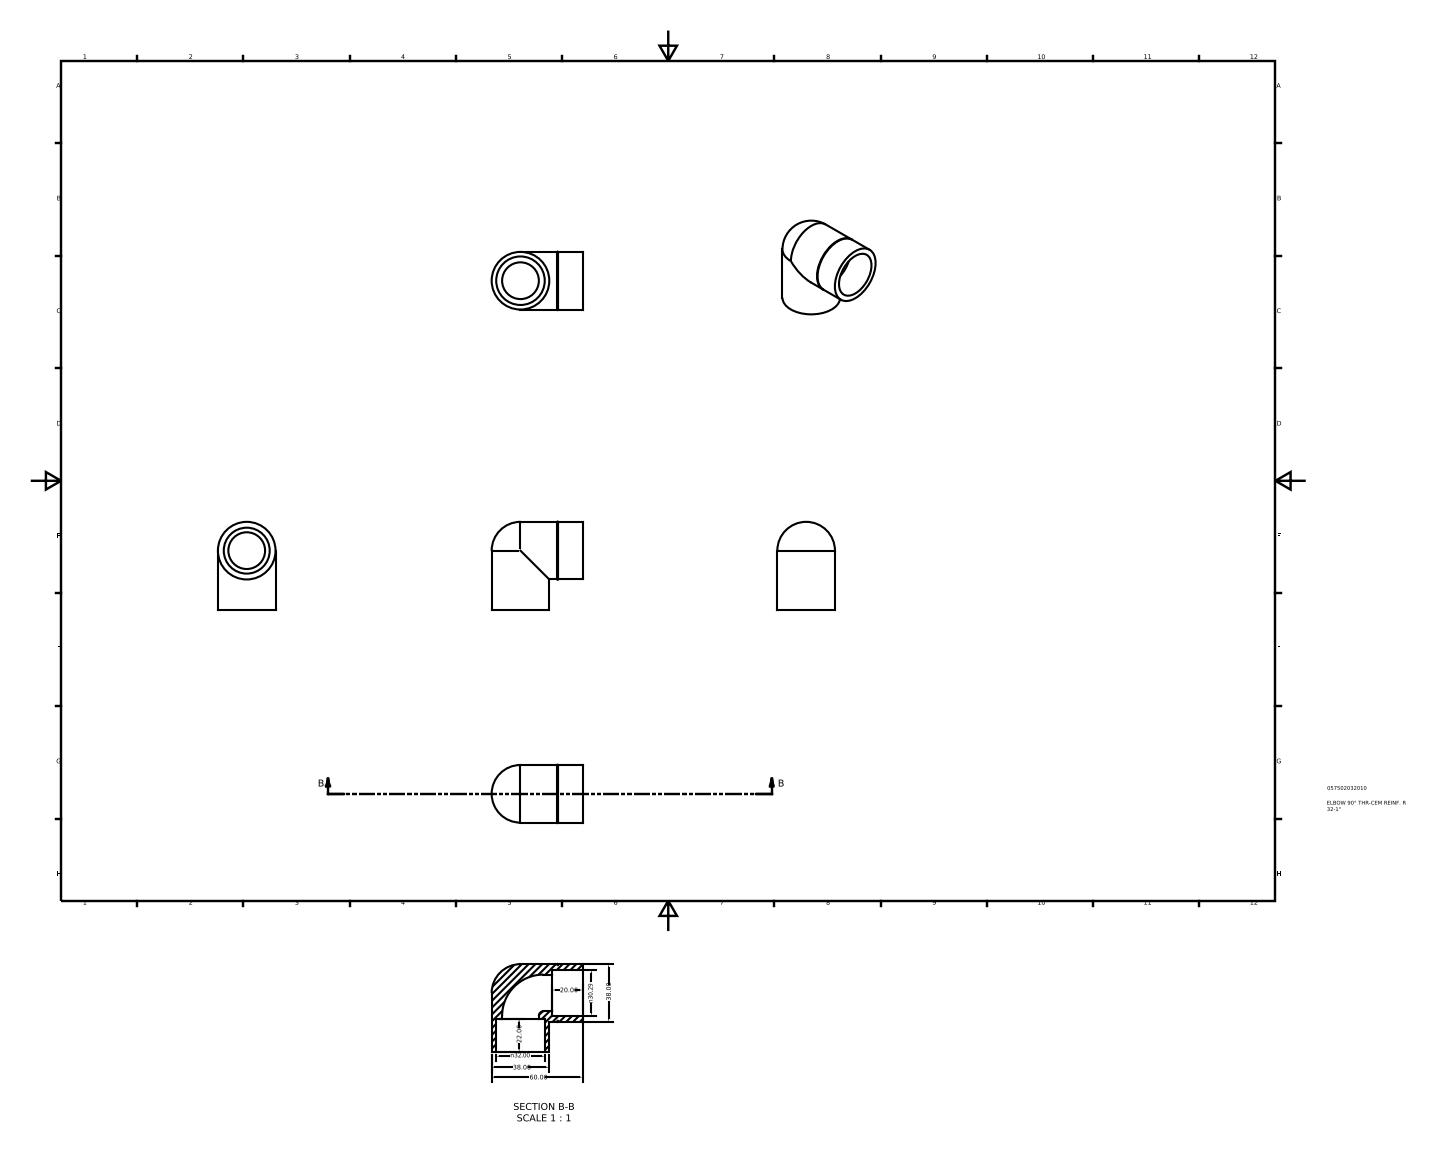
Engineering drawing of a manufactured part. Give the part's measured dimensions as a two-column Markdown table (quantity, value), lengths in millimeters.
| quantity | value |
| --- | --- |
| part name | 057502032010 |
| STEP written by | Autodesk Inventor 2015 (AUTOMOTIVE_DESIGN) |
| units | millimeters |
| bodies | 1 solid, 15 faces (4 planar, 7 cylindrical, 4 other) |
| overall size | 60 × 58 × 38 |
| volume | 42 118 mm³ |
| surface area | 17 171 mm² |
| round holes (diameter × count) | 24.23 × 2, 30.29 × 1, 32 × 1 |
| round bosses / shafts (diameter × count) | 38 × 2 |
| main face-to-face distances | 22, 20 |
